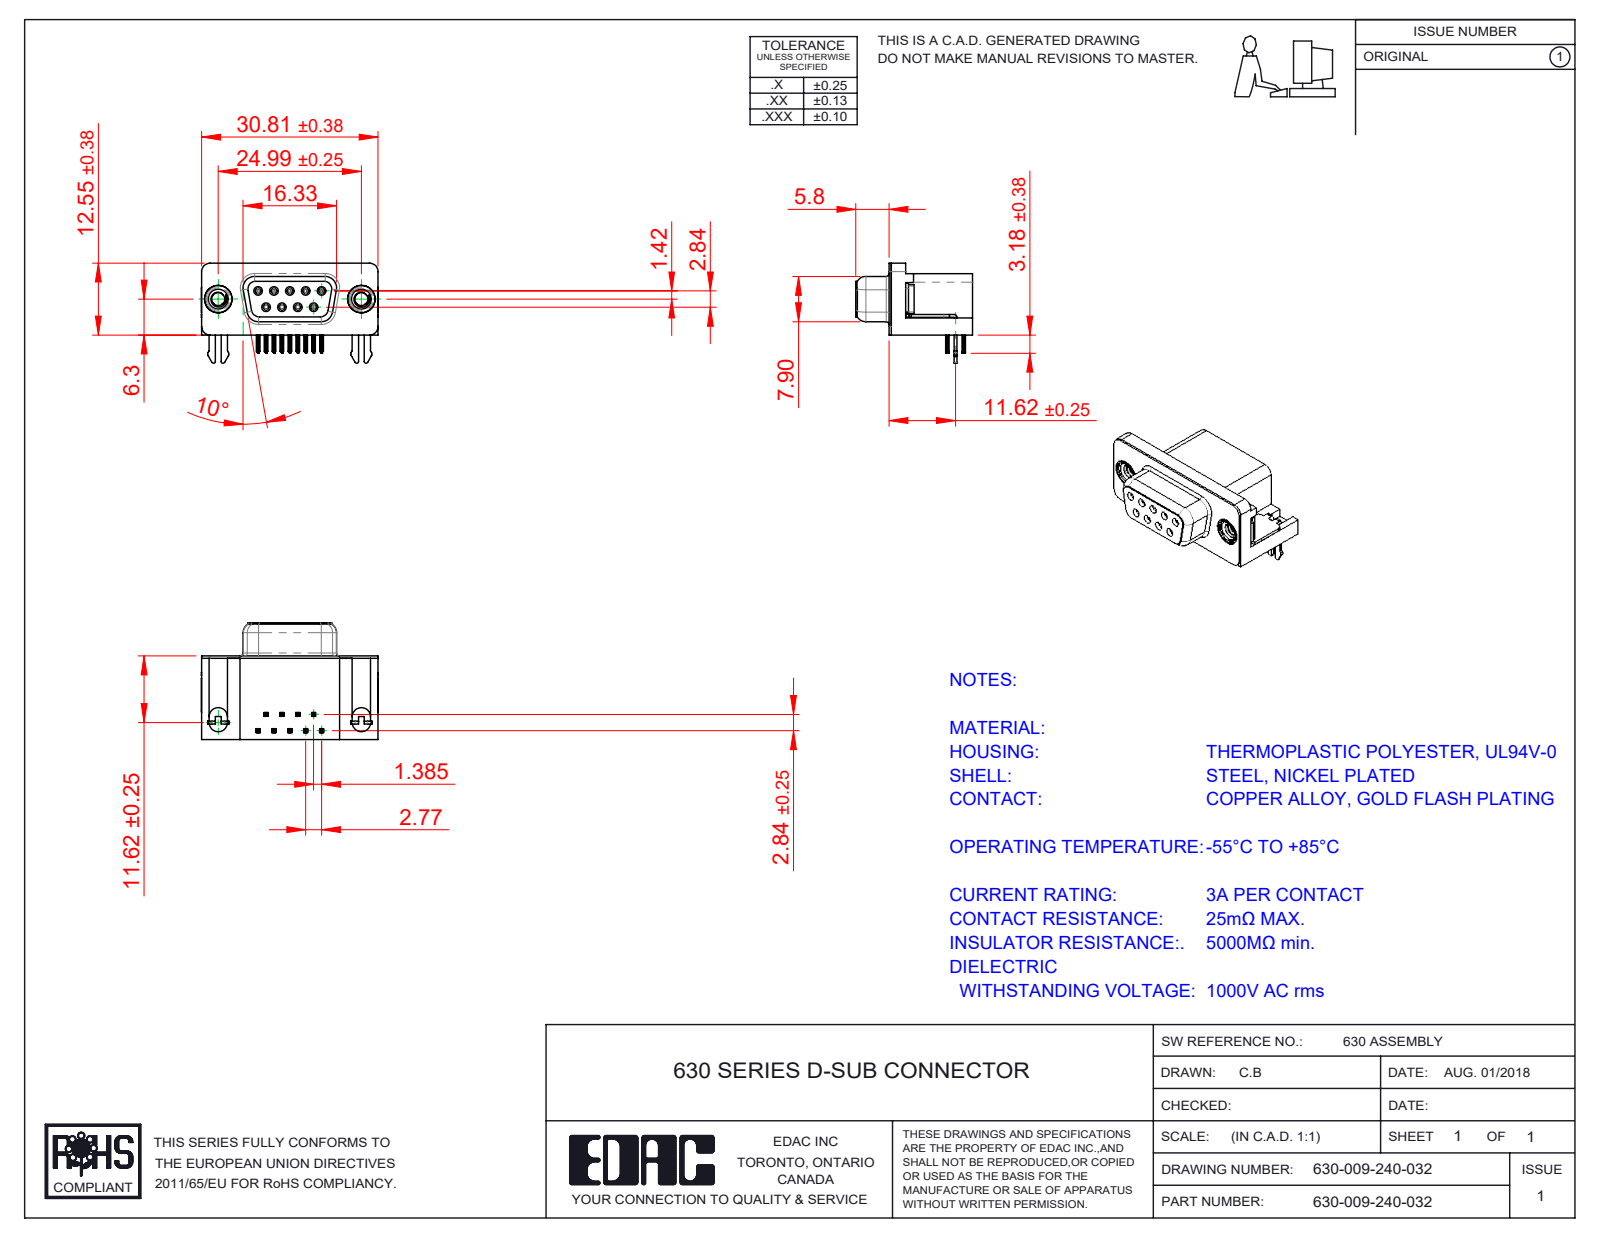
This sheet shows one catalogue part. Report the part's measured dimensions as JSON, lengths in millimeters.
{"part_name": "630 Housing_09 Socket; 630 2 Prong Board Lock; 630-009-240-032; 630 Shell_09 Socket (+3 more)", "step_written_by": "SolidWorks 2020 (CONFIG_CONTROL_DESIGN)", "units": "millimeters", "bodies": {"solids": 15, "faces": 1610, "planar": 714, "cylindrical": 424, "other": 472}, "overall_size": [30.89, 20.4, 17.48], "volume_mm3": 4206, "surface_area_mm2": 5454, "round_holes": [[0.8, 9], [0.9, 9], [2.26, 2], [4, 2], [4.8, 2], [5, 2]], "round_bosses_or_shafts": [[1.2, 9], [4.9, 2], [4.75, 2], [3.9, 2]], "partial_cylinders_radius": [[0.1, 72], [0.15, 36], [0.35, 18], [1, 18], [0.5, 10], [0.34, 9], [0.25, 8], [1.35, 8]], "face_to_face_distances": [0.4, 14.6, 14.2, 10.34, 0.5, 6.2, 2.9, 2.5, 11.7, 0.35], "hole_center_spacings": [3.16, 2.77, 5.54, 5.03, 5.04, 8.31, 7.48, 7.49]}
